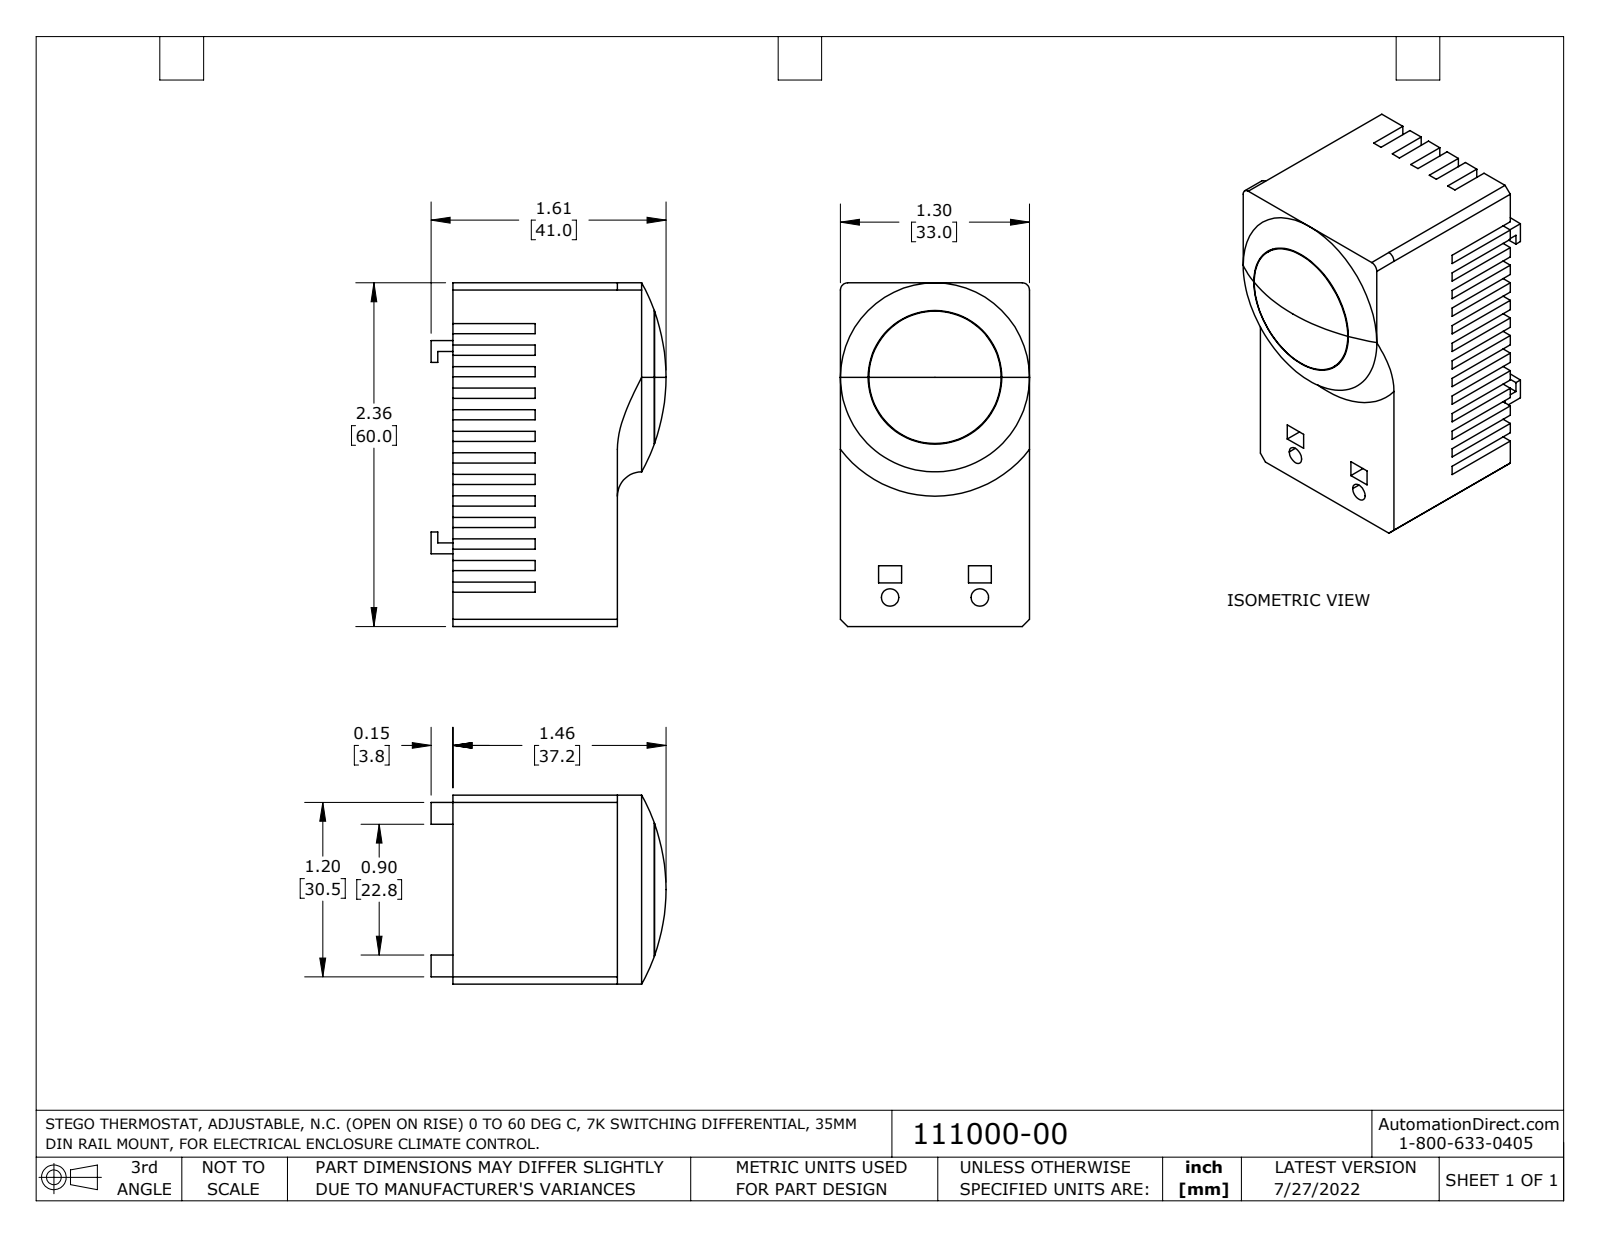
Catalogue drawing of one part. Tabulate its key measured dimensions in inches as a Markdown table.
| quantity | value |
| --- | --- |
| part name | 111000-00_Default |
| STEP written by | SolidWorks 2021 (CONFIG_CONTROL_DESIGN) |
| units | inches |
| bodies | 1 solid, 198 faces (183 planar, 10 cylindrical, 5 other) |
| overall size | 2.362 × 1.614 × 1.299 |
| volume | 3.737 in³ |
| surface area | 19.92 in² |
| round holes (diameter × count) | 0.12 × 2, 0.919 × 1 |
| round bosses / shafts (diameter × count) | 0.909 × 1 |
| partial cylindrical surfaces (radius × count) | 0.05 × 2 |
| main face-to-face distances | 1.299, 0.148, 0.07, 2.362, 0.296, 1.13, 0.444, 0.592, 0.078, 0.218 |
| hole center spacings | 1.544, 0.617 |
